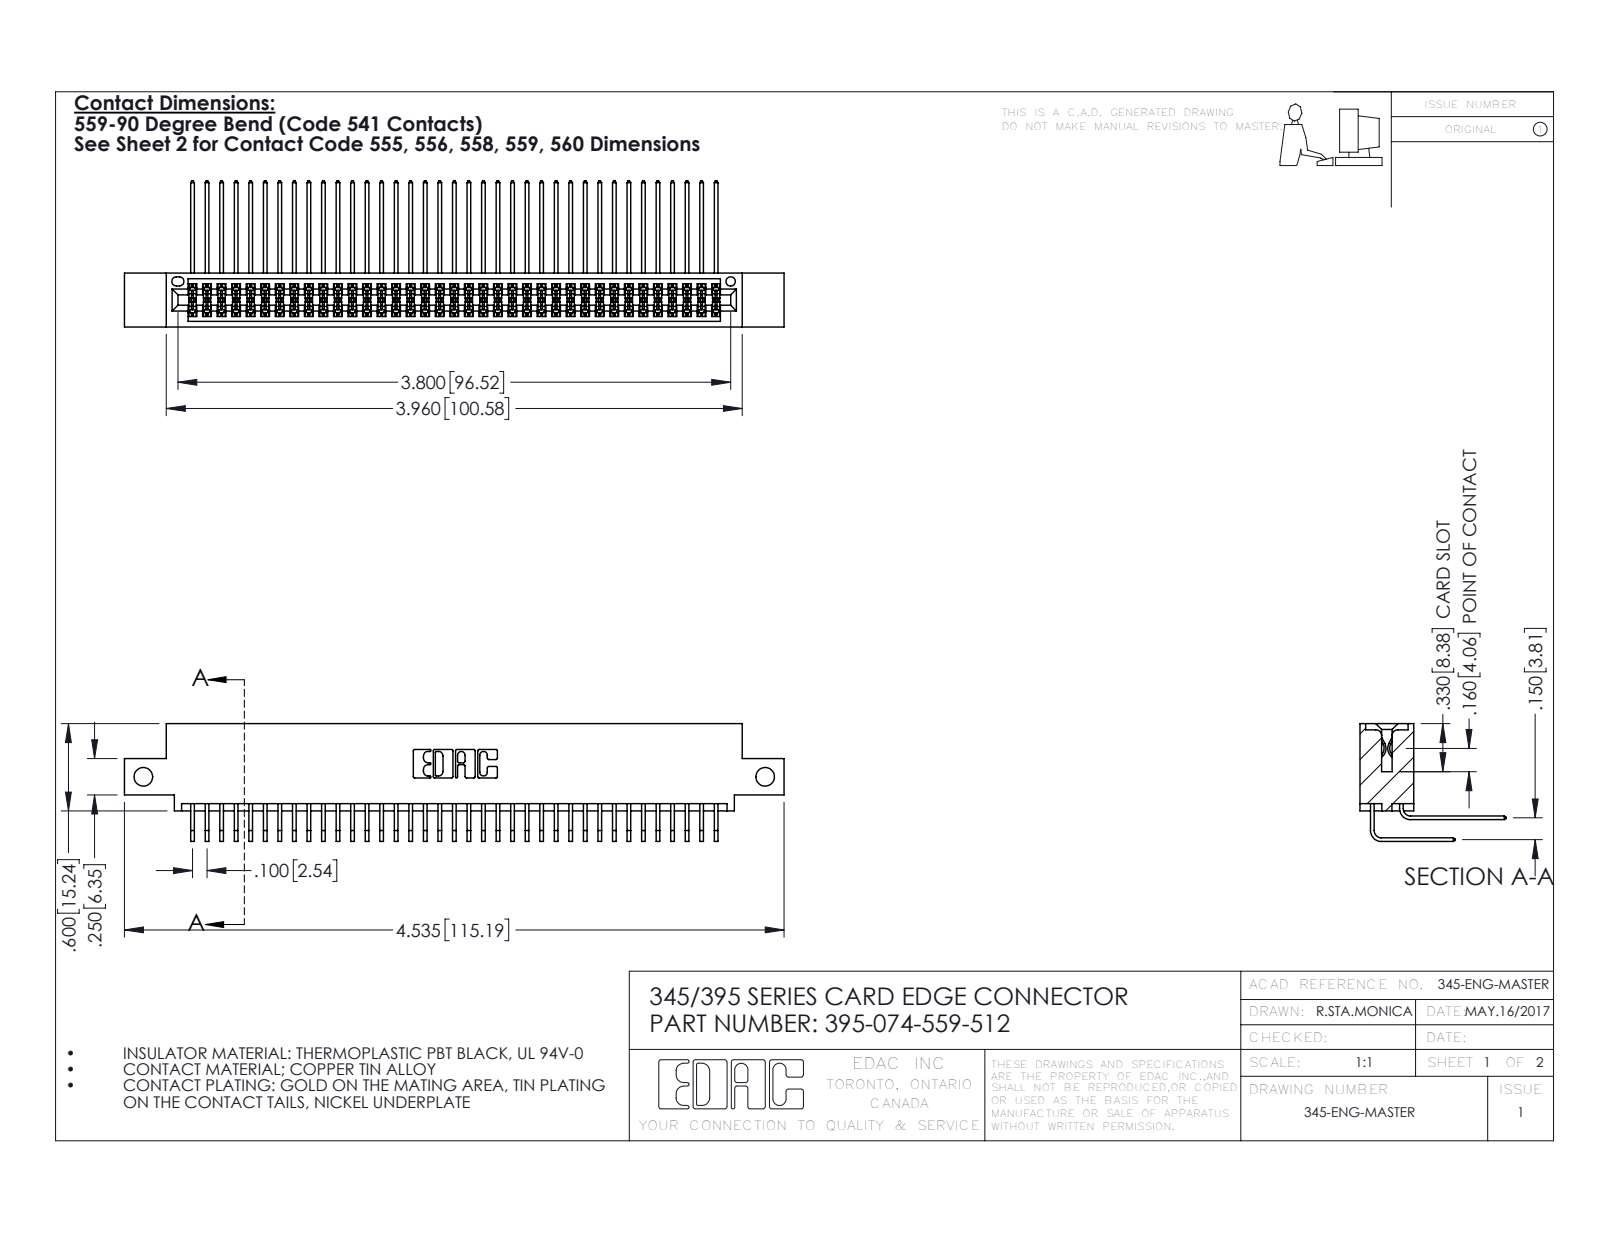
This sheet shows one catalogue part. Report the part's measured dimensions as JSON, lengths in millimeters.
{"part_name": "395-074-559-512; 345-292-001_559 Tail - 2; 345 Part_0.110 Offset - Side Mount; 345-292-001_558 559 Tail - 1", "step_written_by": "SolidWorks 2016 (CONFIG_CONTROL_DESIGN)", "units": "millimeters", "bodies": {"solids": 75, "faces": 3978, "planar": 2674, "cylindrical": 1304, "other": 0}, "overall_size": [115.2, 25.5, 20.5], "volume_mm3": 11400, "surface_area_mm2": 18740, "round_holes": [[3.3, 2], [1.6, 1]], "partial_cylinders_radius": [[0.2, 112], [0.3, 22], [0.2, 6], [0.8, 6], [0.7, 3], [0.4, 2], [0.5, 2], [0.6, 2]], "face_to_face_distances": [1.8, 7.6, 5.1, 9.4, 2.5, 6.9, 0.6, 5.7, 4.4, 3.8], "hole_center_spacings": [108.6]}
